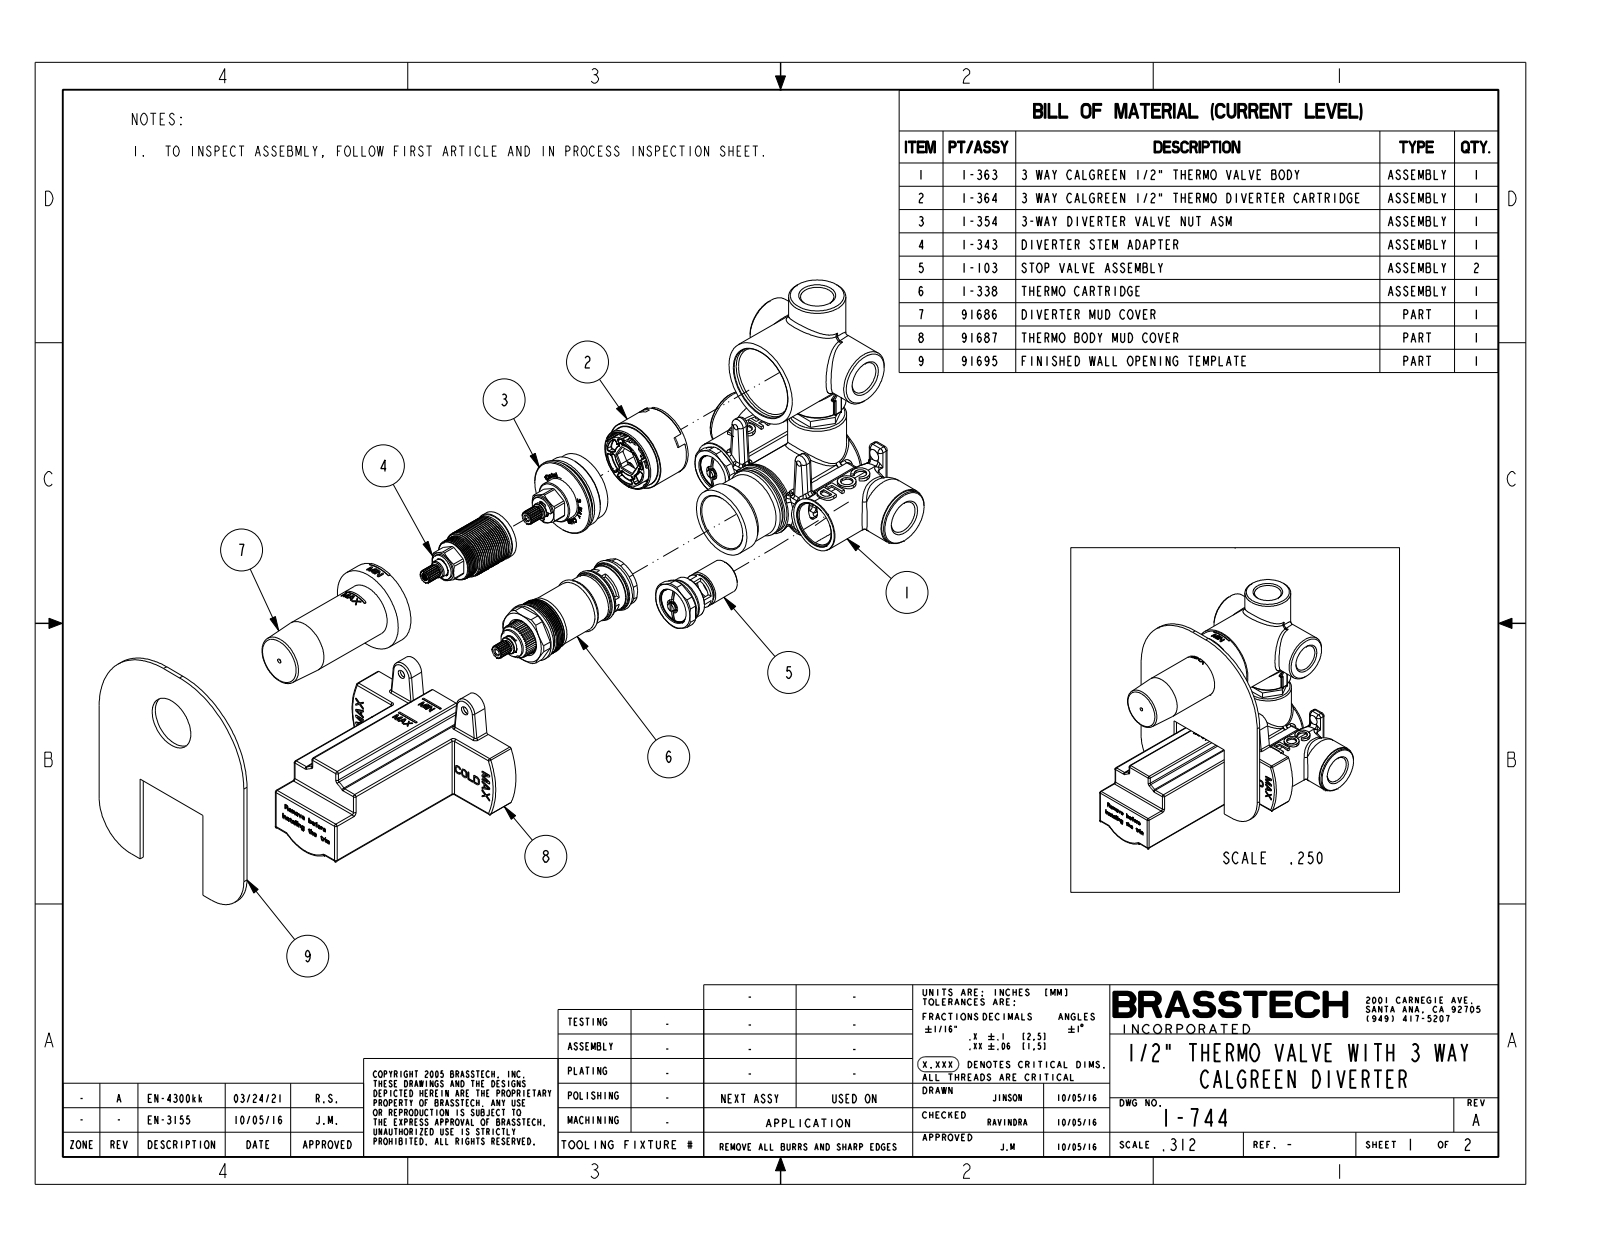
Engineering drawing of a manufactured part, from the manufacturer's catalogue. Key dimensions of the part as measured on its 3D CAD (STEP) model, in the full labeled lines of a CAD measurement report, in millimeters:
Part name (STEP PRODUCT): 1-744_SW0001
STEP written by: CREO PARAMETRIC BY PTC INC, 2018400 (CONFIG_CONTROL_DESIGN)
Units: millimetres
Bodies: 1 solid, 1758 faces (830 planar, 382 cylindrical, 546 other)
Overall size (bounding box): 161.1 × 138 × 121.7
Volume: 469 800 mm³ · Surface area: 65 810 mm²
Round holes (diameter × count): ⌀3.3 ×4, ⌀7 ×2, ⌀8 ×2, ⌀20.5 ×2, ⌀21 ×2, ⌀10 ×1
Round bosses / shafts (diameter × count): ⌀32 ×3, ⌀33 ×2, ⌀24 ×2, ⌀19.9 ×2, ⌀6.5 ×2, ⌀6 ×2, ⌀4.5 ×2, ⌀50 ×1
Partial cylindrical surfaces — rounded edges, fillets, slot ends (radius × count): R2 ×43, R0.5 ×38, R1 ×4, R1.8 ×2, R3.9 ×2, R4 ×2, R5.3 ×2, R7.5 ×2
Main face-to-face distances: 107, 31, 2, 47.5, 27, 76, 63.2, 138, 54.5, 7
Hole centre spacings: 17.2, 21.2, 37.3, 38, 40.8, 43, 51.5, 61.6
